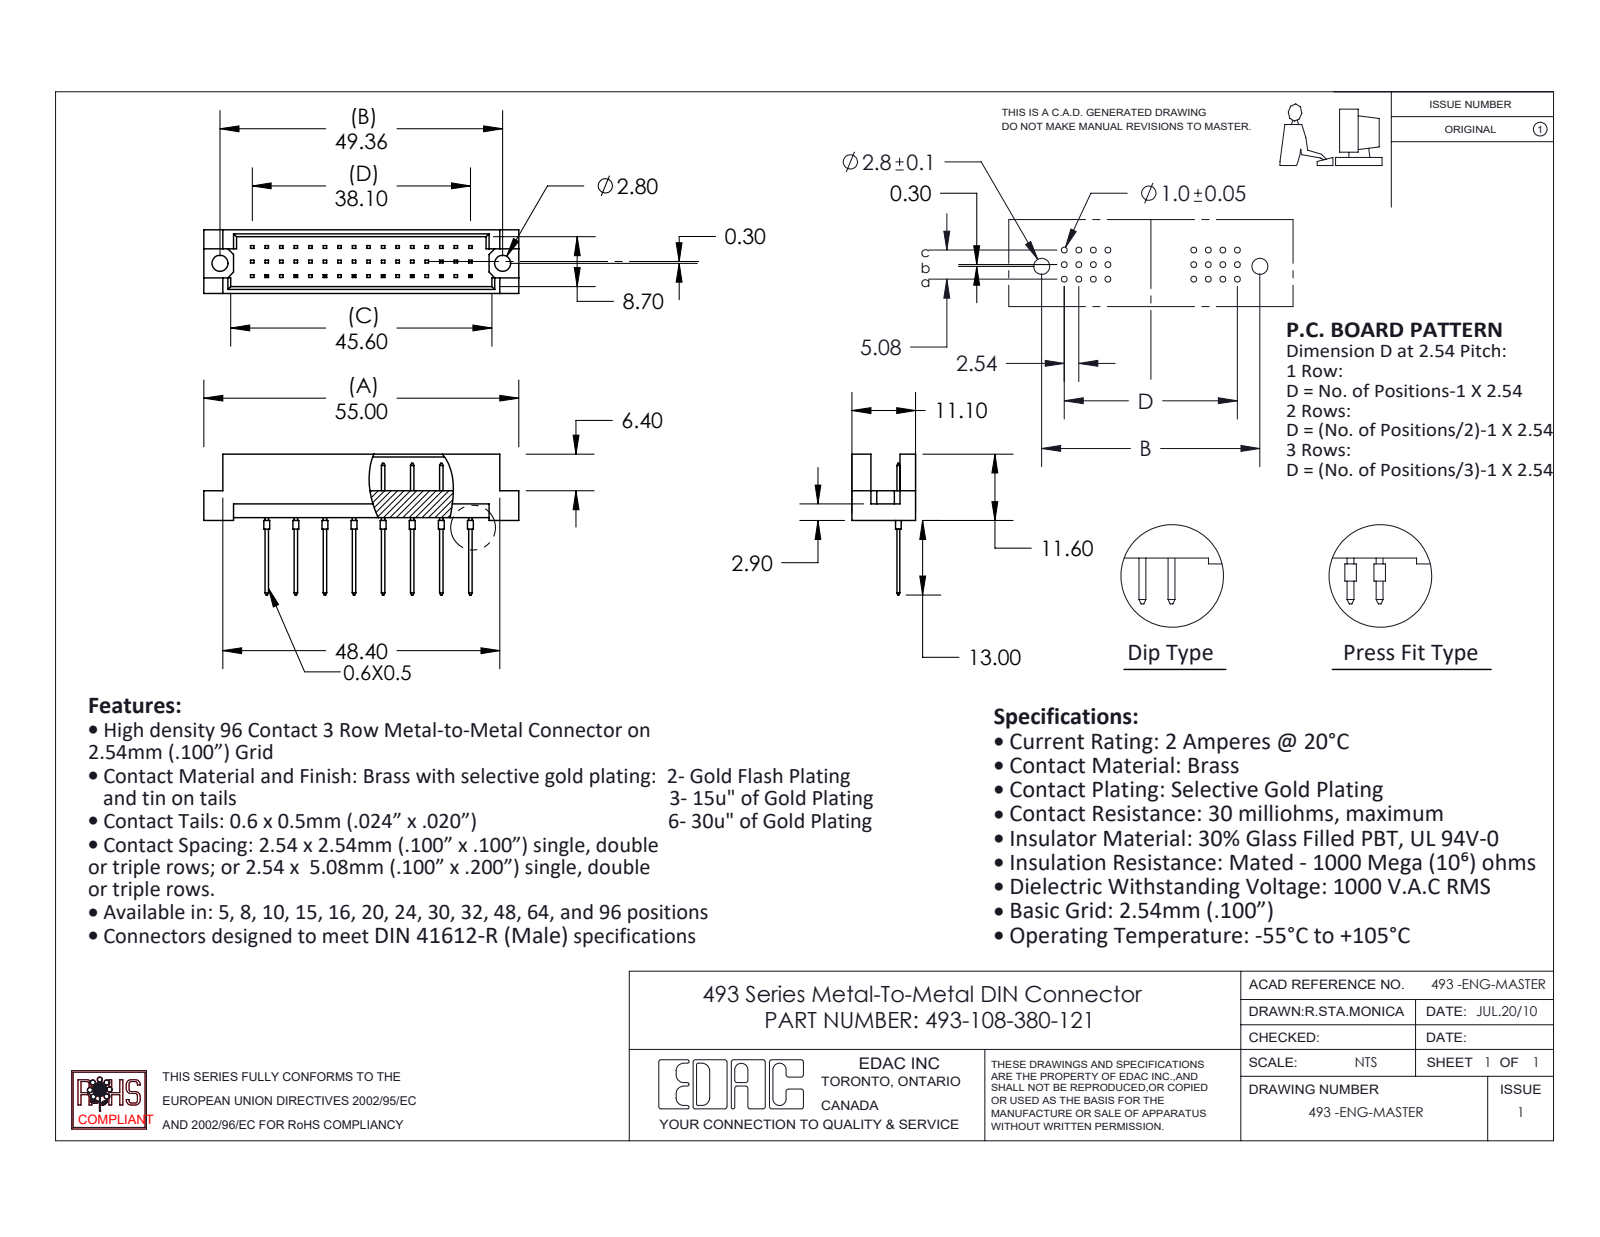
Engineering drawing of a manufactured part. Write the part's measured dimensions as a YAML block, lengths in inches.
part_name: "493-108-380-122; 493 Part_48; 493-290_80"
step_written_by: "SolidWorks 2020 (CONFIG_CONTROL_DESIGN)"
units: inches
bodies: {solids: 9, faces: 420, planar: 400, cylindrical: 20, other: 0}
overall_size: [2.165, 0.969, 0.437]
volume: 0.203
surface_area: 6.474
round_holes:
  - {diameter: 0.11, count: 2}
round_bosses_or_shafts:
  - {diameter: 0.039, count: 8}
face_to_face_distances: [0.047, 0.39, 0.437, 0.343, 0.185, 0.02, 0.2, 0.109, 0.328, 0.061]
hole_center_spacings: [1.943]
